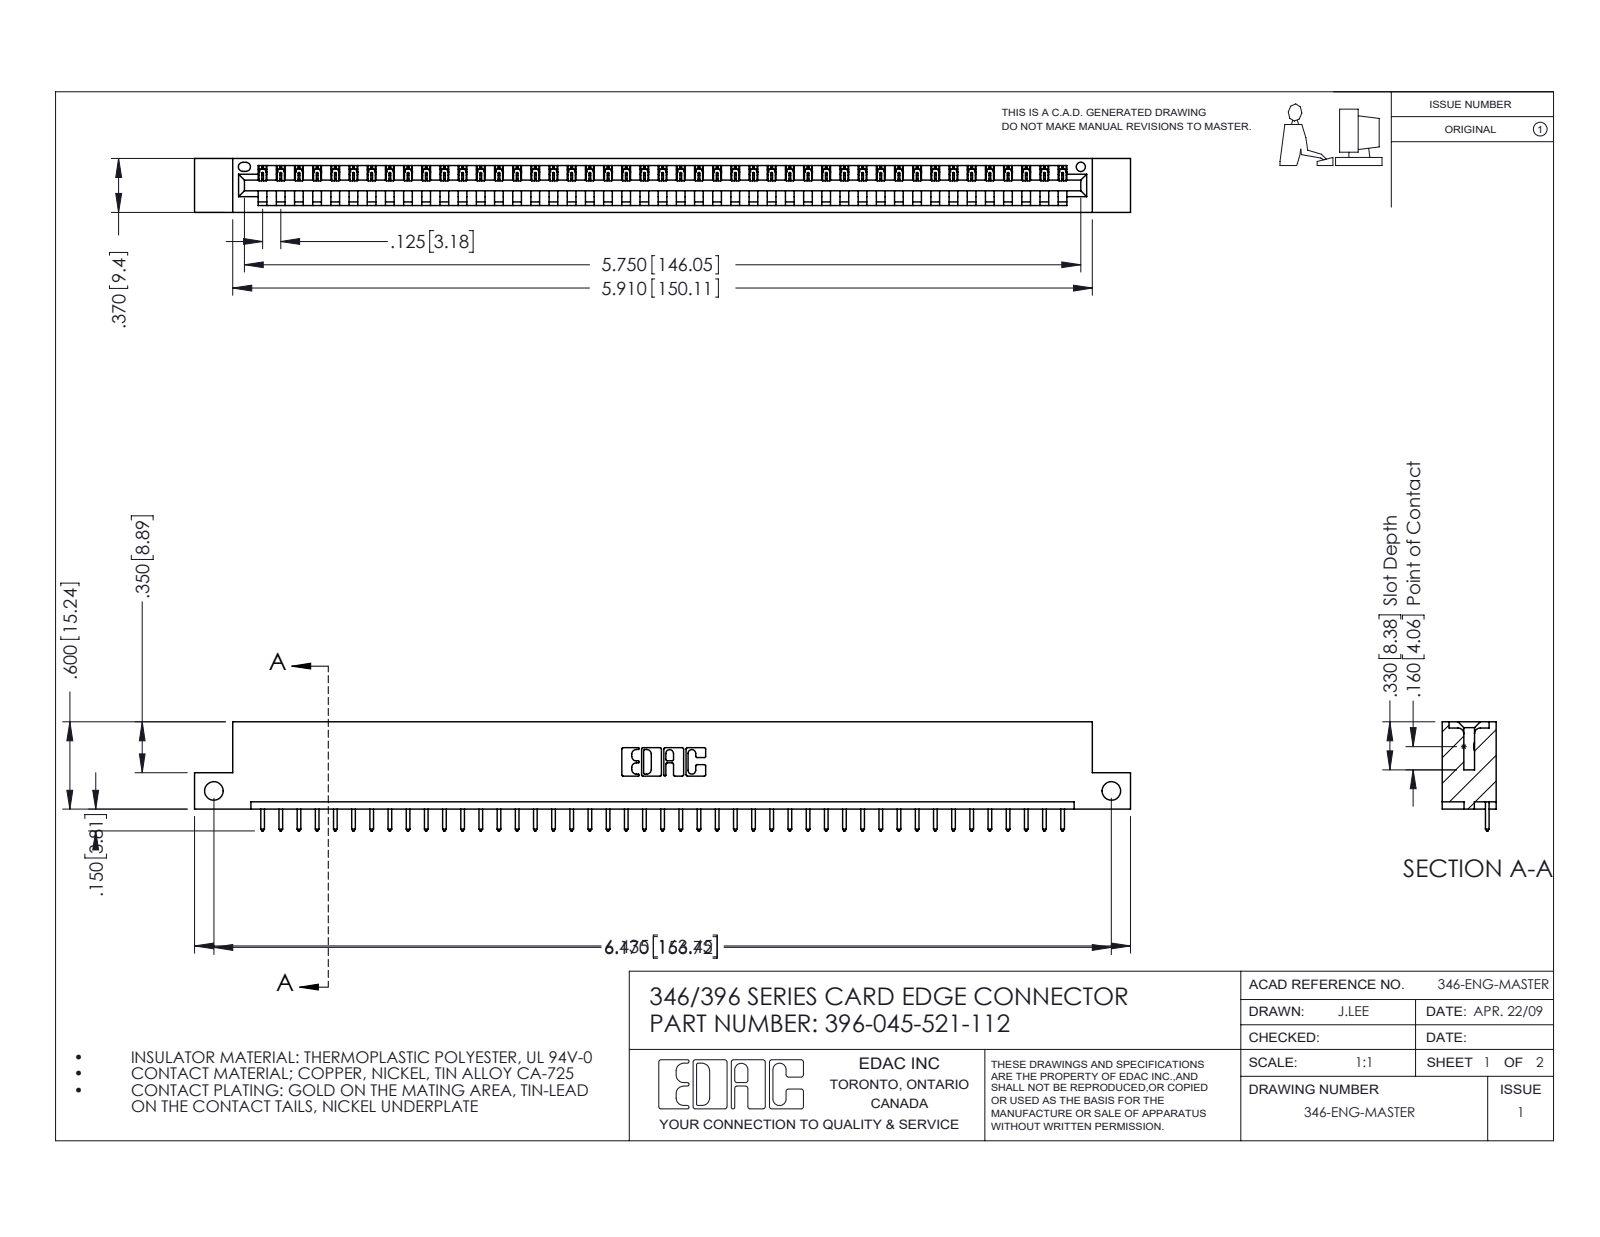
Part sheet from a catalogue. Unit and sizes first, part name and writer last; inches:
Units: inches
Overall size (bounding box): 6.435 × 0.75 × 0.37
Round holes (diameter × count): ⌀0.128 ×2, ⌀0.064 ×1
Partial cylindrical surfaces — rounded edges, fillets, slot ends (radius × count): R0.006 ×90, R0.01 ×90, R0.01 ×22, R0.007 ×6, R0.031 ×6, R0.026 ×3, R0.031 ×2, R0.04 ×2
Main face-to-face distances: 0.048, 0.322, 0.37, 0.25, 0.072, 0.298, 0.025, 0.148, 0.222, 0.1
Hole centre spacings: 6.17
Volume: 0.943 in³ · Surface area: 28.97 in²
Bodies: 46 solids, 2732 faces (1876 planar, 856 cylindrical, 0 other)
Part name (STEP PRODUCT): 345-292-001_345-293-121; 396-045-521-112; 346 Part_Flush Mounting Lugs - Side Mount
STEP written by: SolidWorks 2016 (CONFIG_CONTROL_DESIGN)
